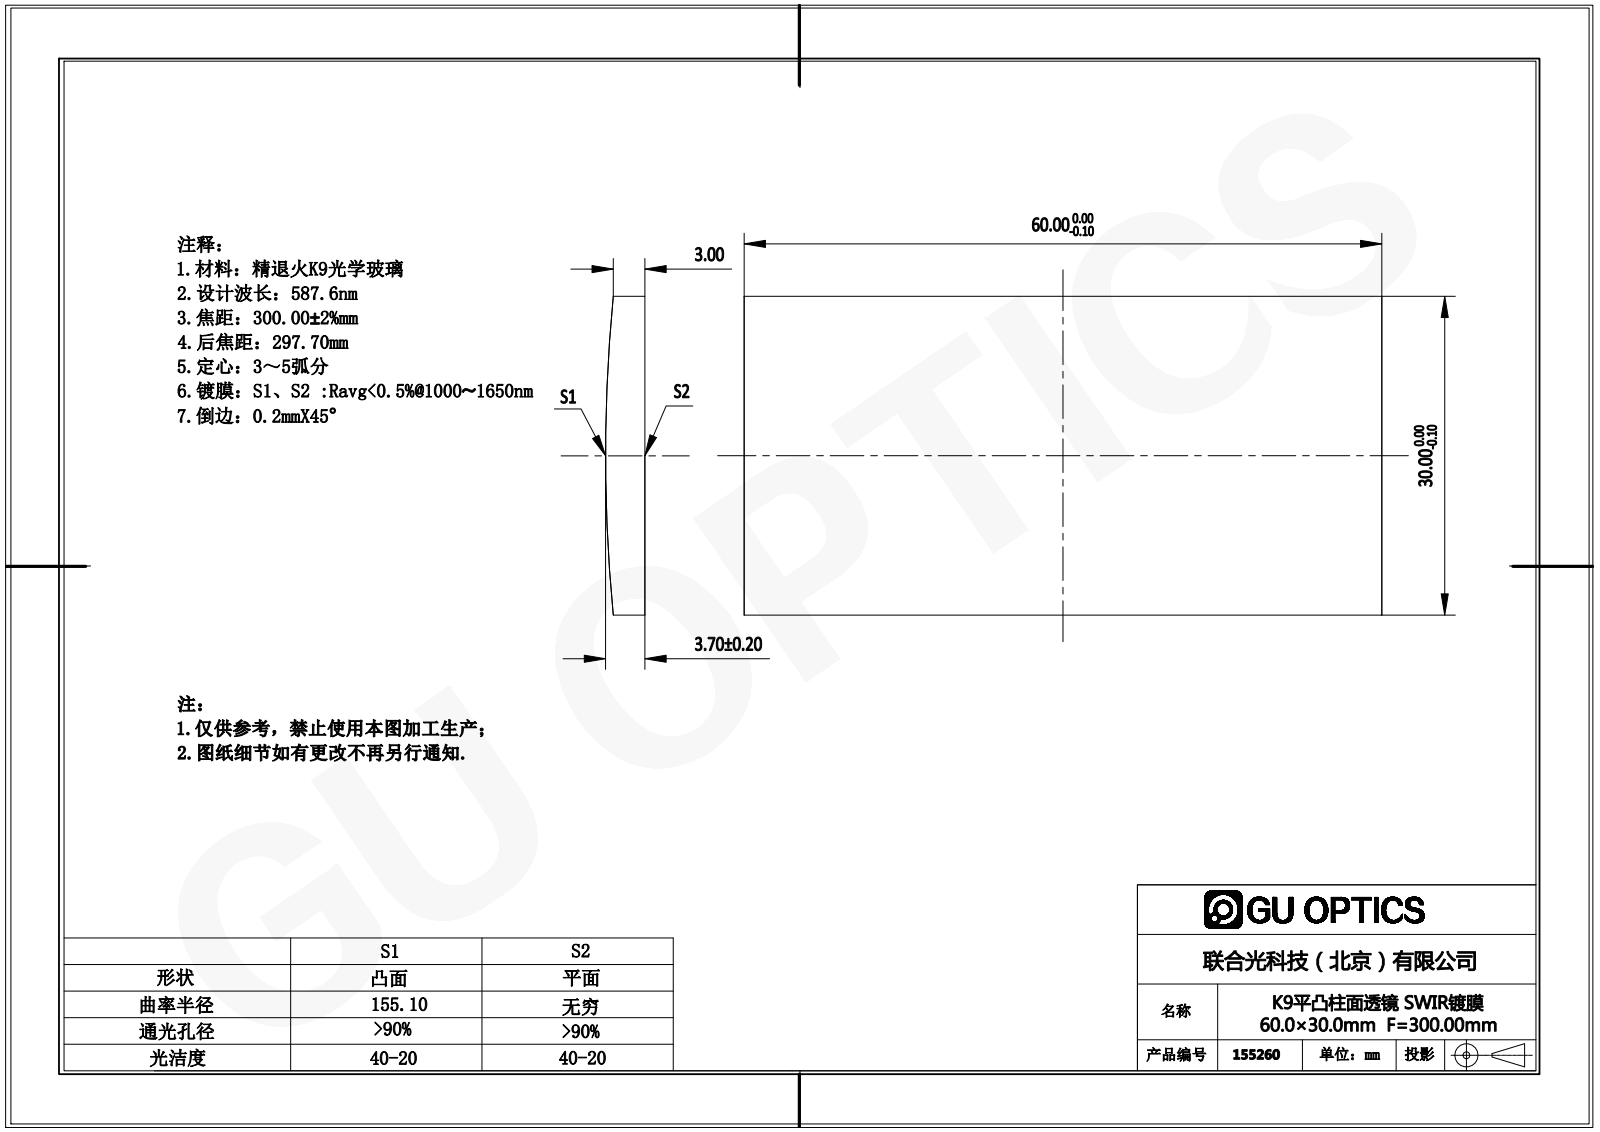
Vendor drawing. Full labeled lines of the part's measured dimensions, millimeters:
Part name (STEP PRODUCT): 155062
STEP written by: SolidWorks 2016 (AUTOMOTIVE_DESIGN)
Units: millimetres
Bodies: 1 solid, 6 faces (5 planar, 1 cylindrical, 0 other)
Overall size (bounding box): 60 × 30 × 3.7
Volume: 6 224 mm³ · Surface area: 4 167 mm²
Partial cylindrical surfaces — rounded edges, fillets, slot ends (radius × count): R155.1 ×1
Main face-to-face distances: 30, 60
